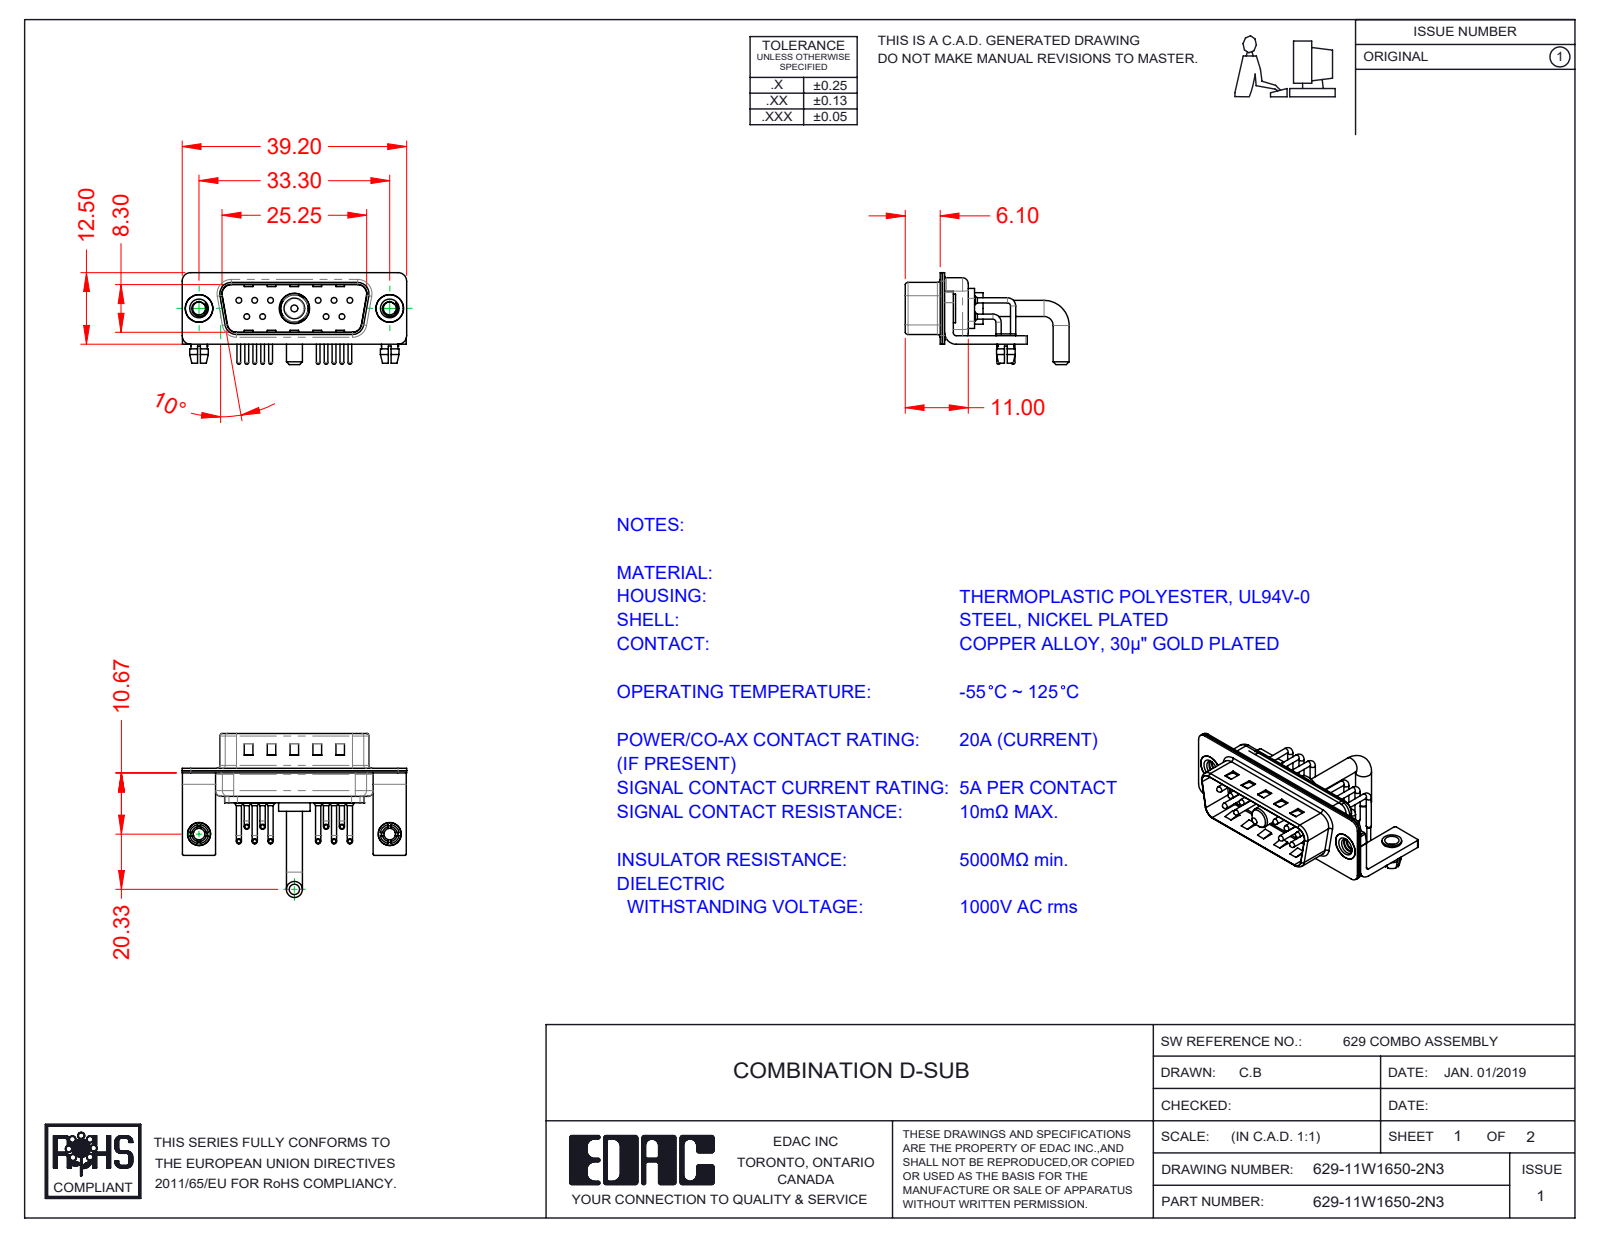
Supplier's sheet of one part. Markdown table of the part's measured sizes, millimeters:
| quantity | value |
| --- | --- |
| part name | 629Combo Contact Row 2; 629Combo Shell Rear_15 Contacts; 629Combo Shell Front_15 Contacts; 629Combo Contact Row 1 (+6 more) |
| STEP written by | SolidWorks 2020 (CONFIG_CONTROL_DESIGN) |
| units | millimeters |
| bodies | 21 solids, 1628 faces (866 planar, 568 cylindrical, 194 other) |
| overall size | 39.2 × 28.63 × 16.05 |
| volume | 2 411 mm³ |
| surface area | 6 093 mm² |
| round holes (diameter × count) | 2 × 12, 0.75 × 10, 1.6 × 10, 2.26 × 2, 2.5 × 2, 3.2 × 2, 4 × 2, 4.8 × 2, 4.85 × 1, 5.3 × 1 |
| round bosses / shafts (diameter × count) | 0.9 × 20, 1.5 × 10, 1 × 10, 0.65 × 10, 5 × 2, 4.9 × 2, 4 × 2, 3.4 × 2 |
| partial cylindrical surfaces (radius × count) | 0.25 × 16, 1.5 × 16, 2 × 13, 1.01 × 10, 0.5 × 9, 1.6 × 8, 1 × 7, 0.6 × 4 |
| main face-to-face distances | 0.4, 0.8, 1.5, 9.5, 9.1, 8.7, 9.9, 0.6, 1.9, 0.75 |
| hole center spacings | 3.16, 2.77, 13.85, 11.08, 16.62, 5.03, 5.04, 5.54 |
